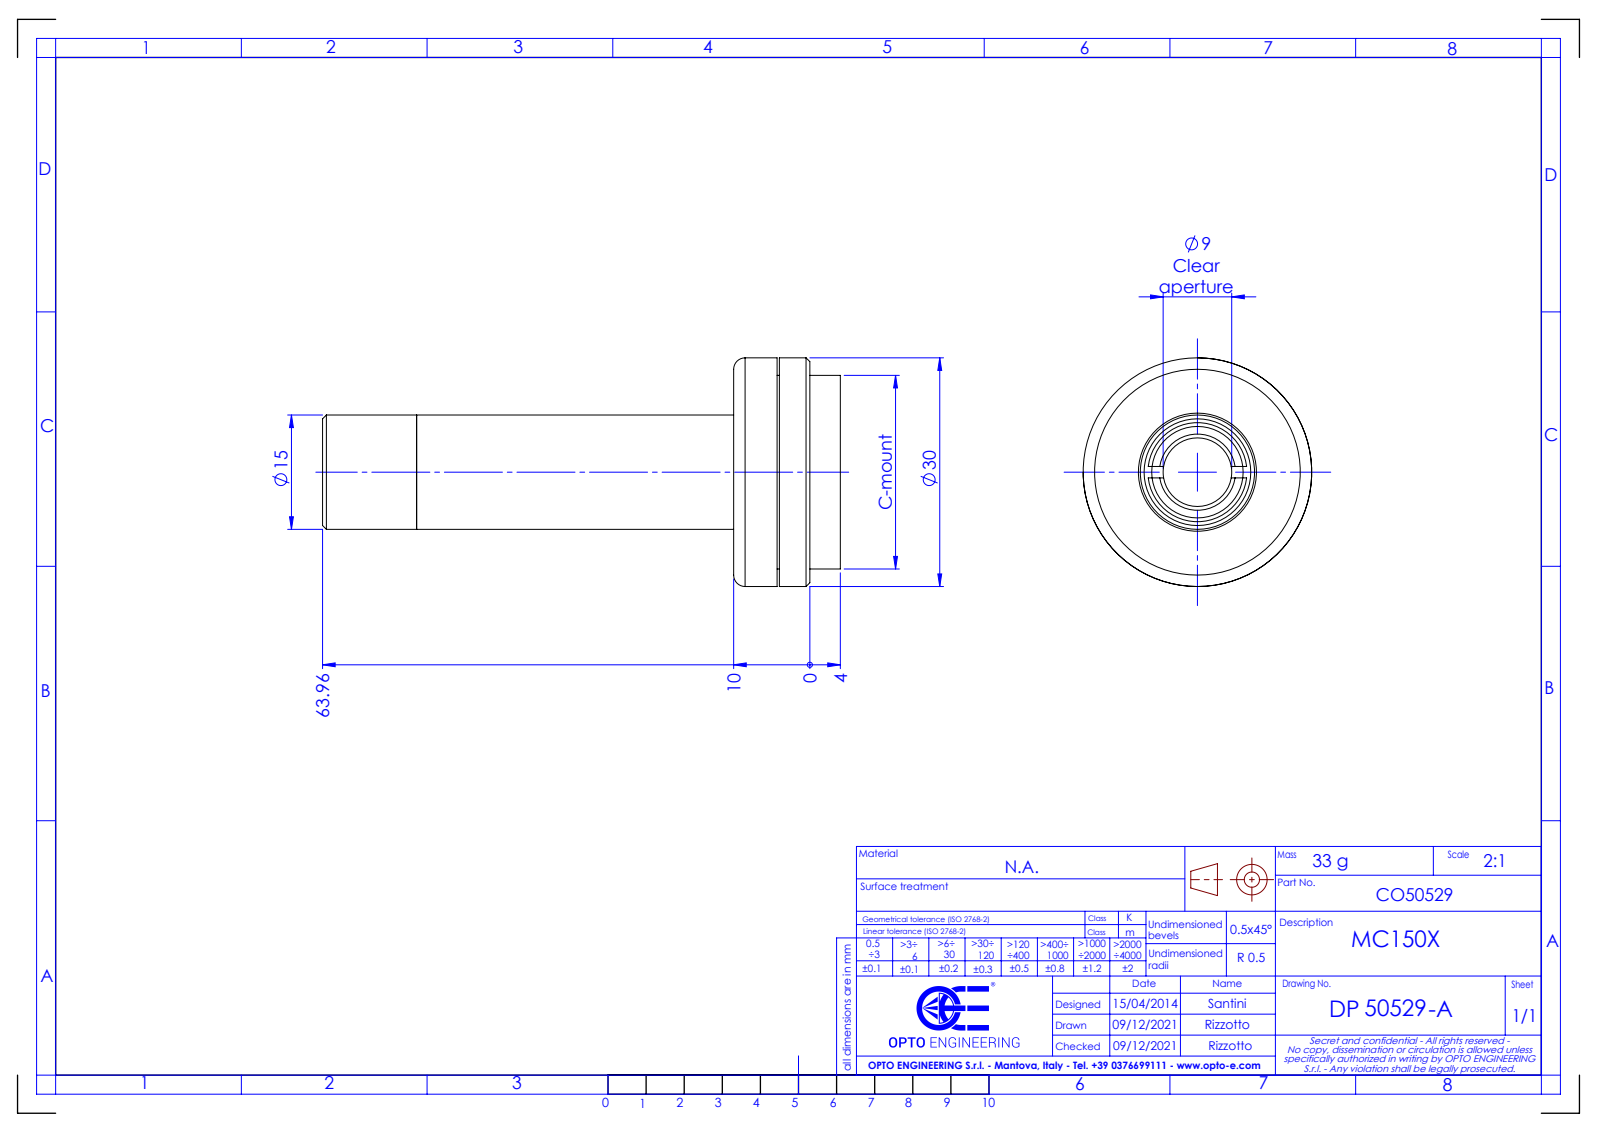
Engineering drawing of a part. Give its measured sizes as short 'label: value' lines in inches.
name: DP50529-A_MC150X
written by: SolidWorks 2021 (CONFIG_CONTROL_DESIGN)
unit: in
bodies: 0 solids, 49 faces (16 planar, 18 cylindrical, 15 other)
size: 2.676 × 1.181 × 1.181
holes: 1× ⌀0.354, 1× ⌀0.472
bosses: 1× ⌀1.181, 1× ⌀1, 1× ⌀0.591, 1× ⌀0.571
face distances: 0.157, 0.236, 0.224, 0.394, 0.169, 0.551, 0.327, 0.315, 2.124, 2.349
